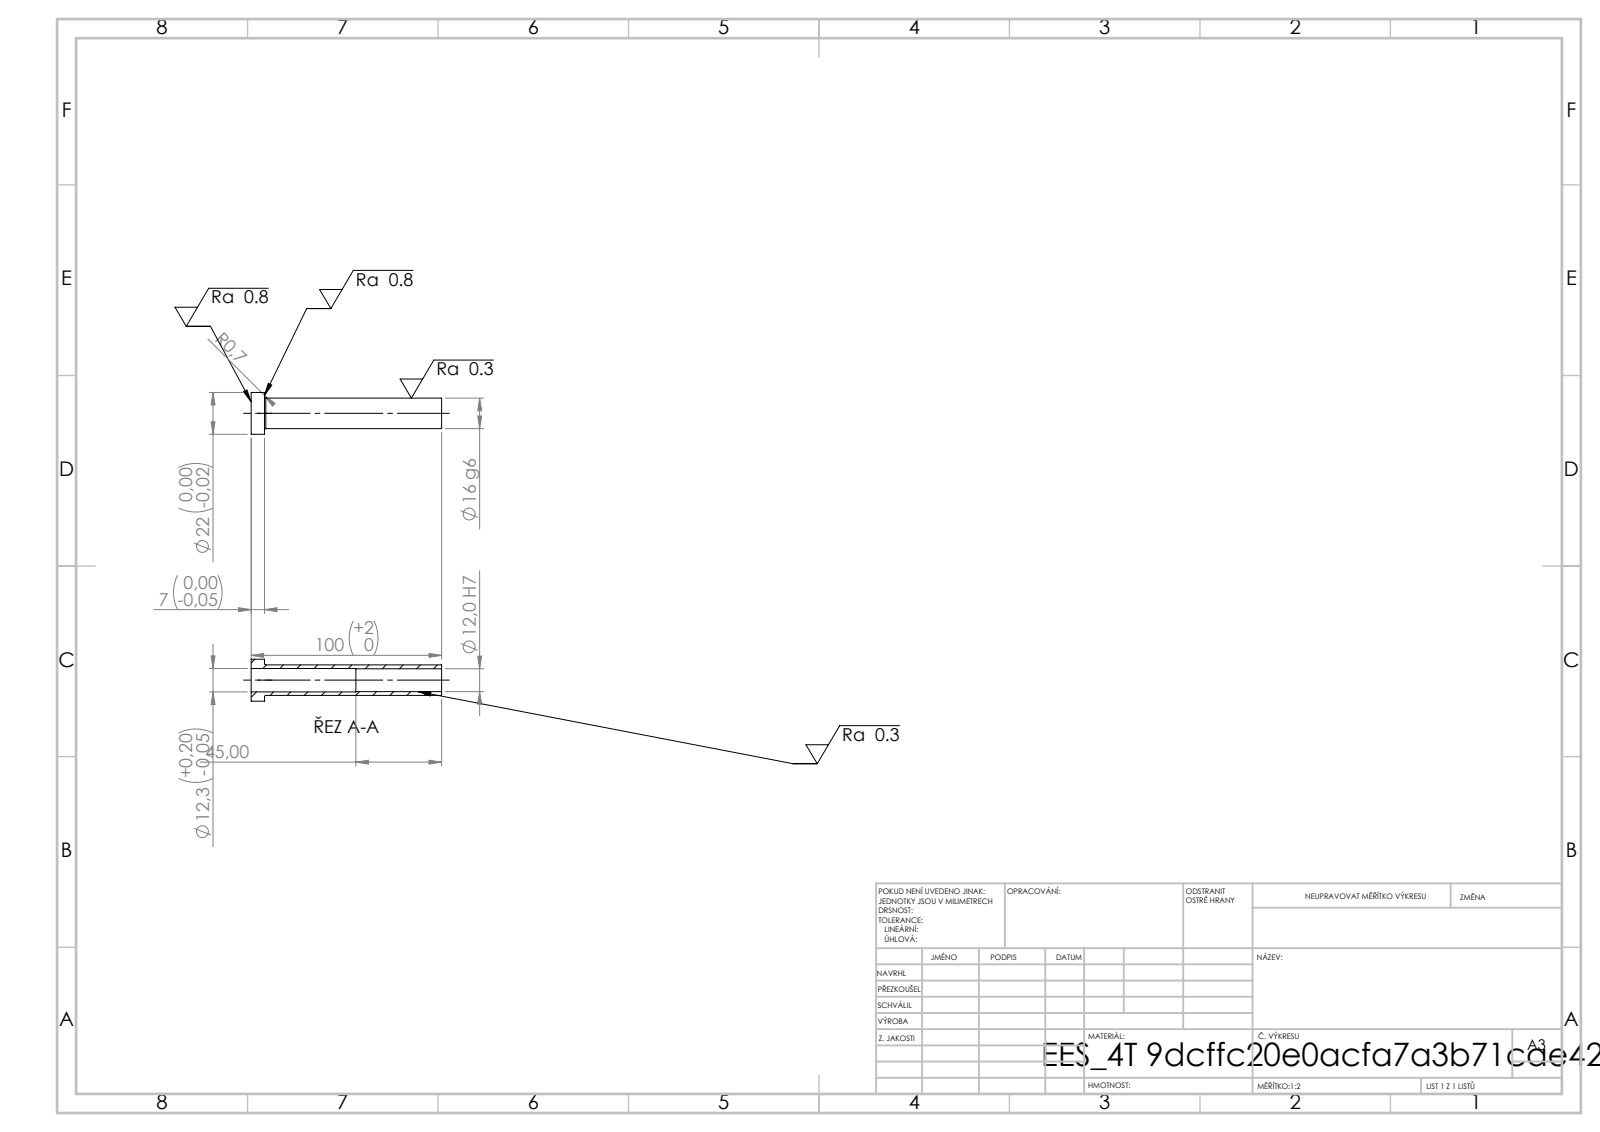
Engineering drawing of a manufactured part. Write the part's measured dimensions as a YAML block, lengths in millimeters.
step_written_by: "SolidWorks 2019 (CONFIG_CONTROL_DESIGN)"
units: millimeters
bodies: {solids: 1, faces: 14, planar: 4, cylindrical: 8, other: 2}
overall_size: [100, 22, 22]
volume: 9740
surface_area: 9499
round_holes:
  - {diameter: 12, count: 1}
  - {diameter: 12.3, count: 1}
round_bosses_or_shafts:
  - {diameter: 22, count: 1}
  - {diameter: 16, count: 1}
face_to_face_distances: [7, 100, 93, 55, 48, 45]
